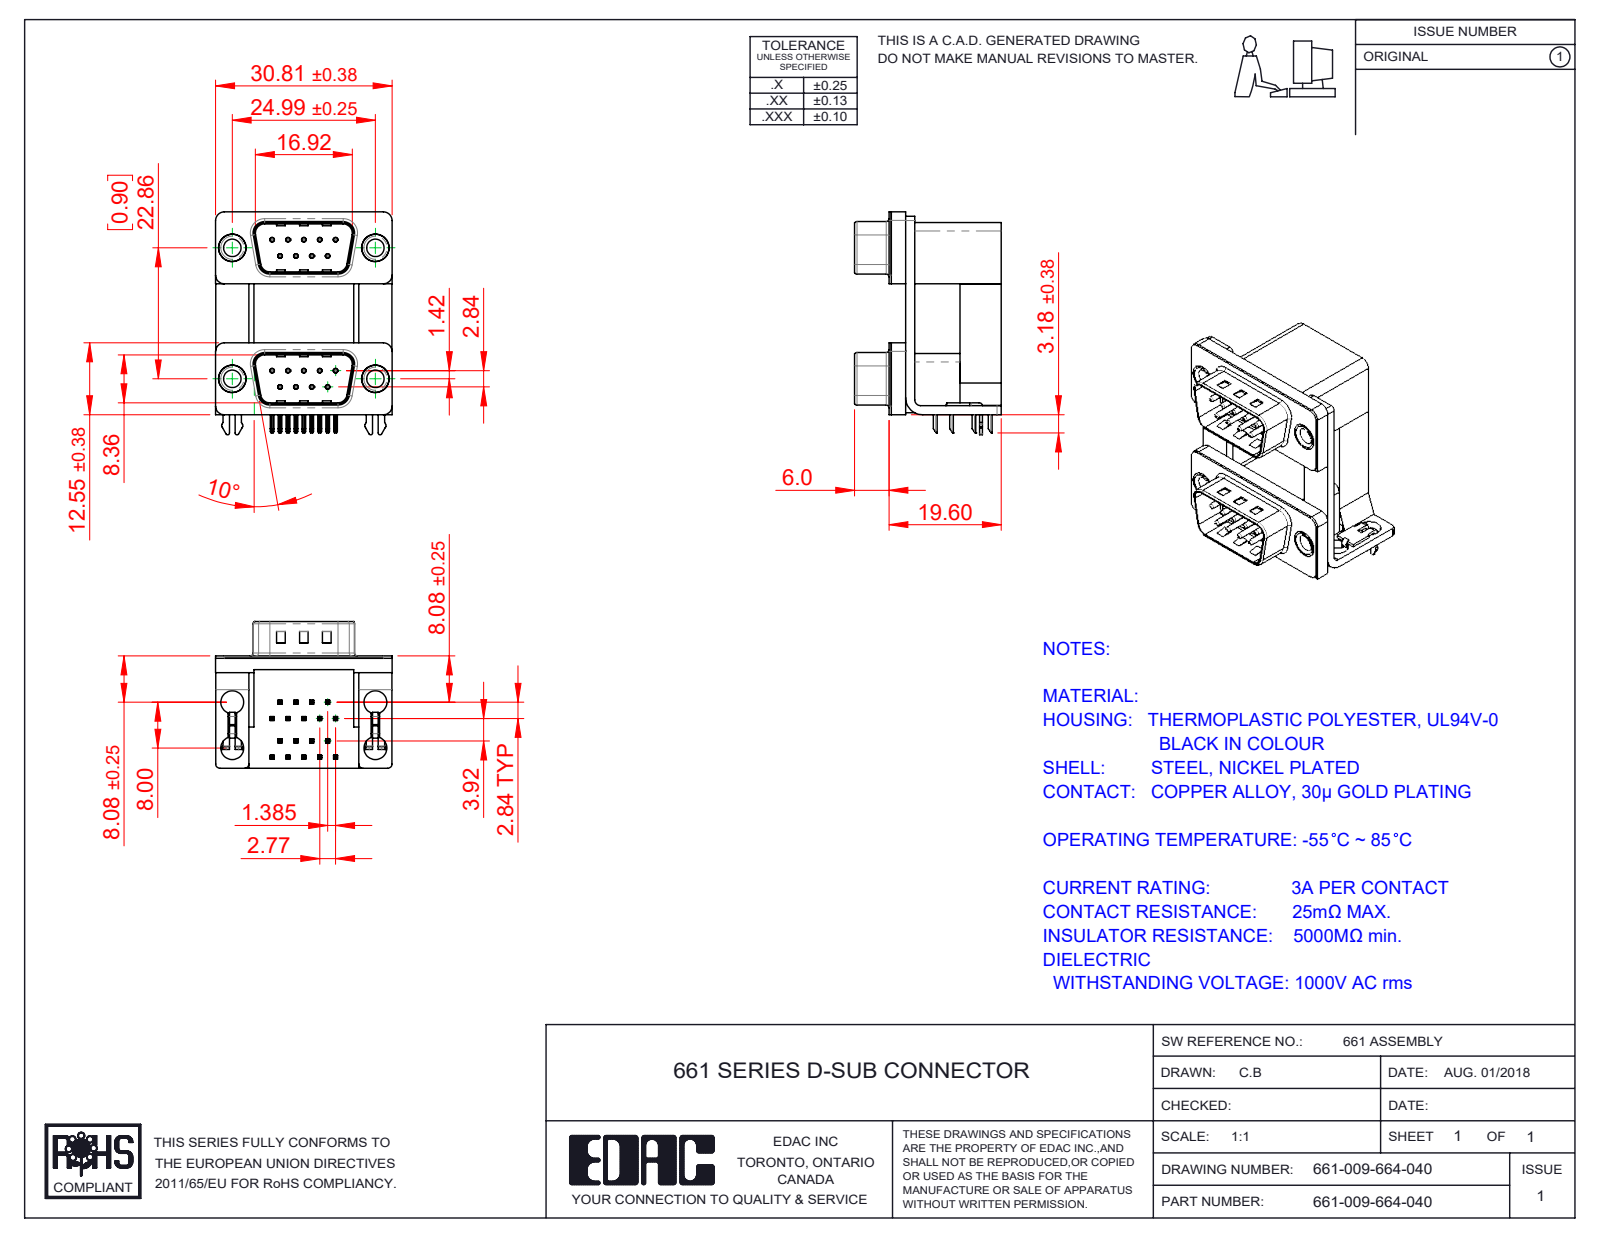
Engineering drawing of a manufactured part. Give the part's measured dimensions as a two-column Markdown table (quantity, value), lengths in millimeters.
| quantity | value |
| --- | --- |
| part name | 661 Contact Bottom Lower; 661 Housing Spacer_09 Contacts H; 661 Mounting Bracket_2ProngH; 661-009-664-040 (+8 more) |
| STEP written by | SolidWorks 2020 (CONFIG_CONTROL_DESIGN) |
| units | millimeters |
| bodies | 31 solids, 1972 faces (1230 planar, 588 cylindrical, 154 other) |
| overall size | 38.91 × 30.81 × 25.6 |
| volume | 10 794 mm³ |
| surface area | 12 440 mm² |
| round holes (diameter × count) | 0.35 × 18, 0.8 × 18, 4 × 8, 3.05 × 4, 3.5 × 4, 4.8 × 4, 5 × 4 |
| round bosses / shafts (diameter × count) | 0.75 × 18, 4.9 × 4, 4.75 × 4, 3.85 × 4 |
| partial cylindrical surfaces (radius × count) | 0.25 × 78, 0.12 × 36, 0.5 × 20, 1.5 × 14, 0.75 × 10, 0.9 × 8, 1.6 × 8, 2 × 8 |
| main face-to-face distances | 0.4, 2.5, 22.86, 12, 16.7, 19.2, 7.2, 9.5, 12.4, 1.6 |
| hole center spacings | 3.16, 2.77, 23.03, 22.86, 5.54, 23.52, 20.07, 25.74 |
